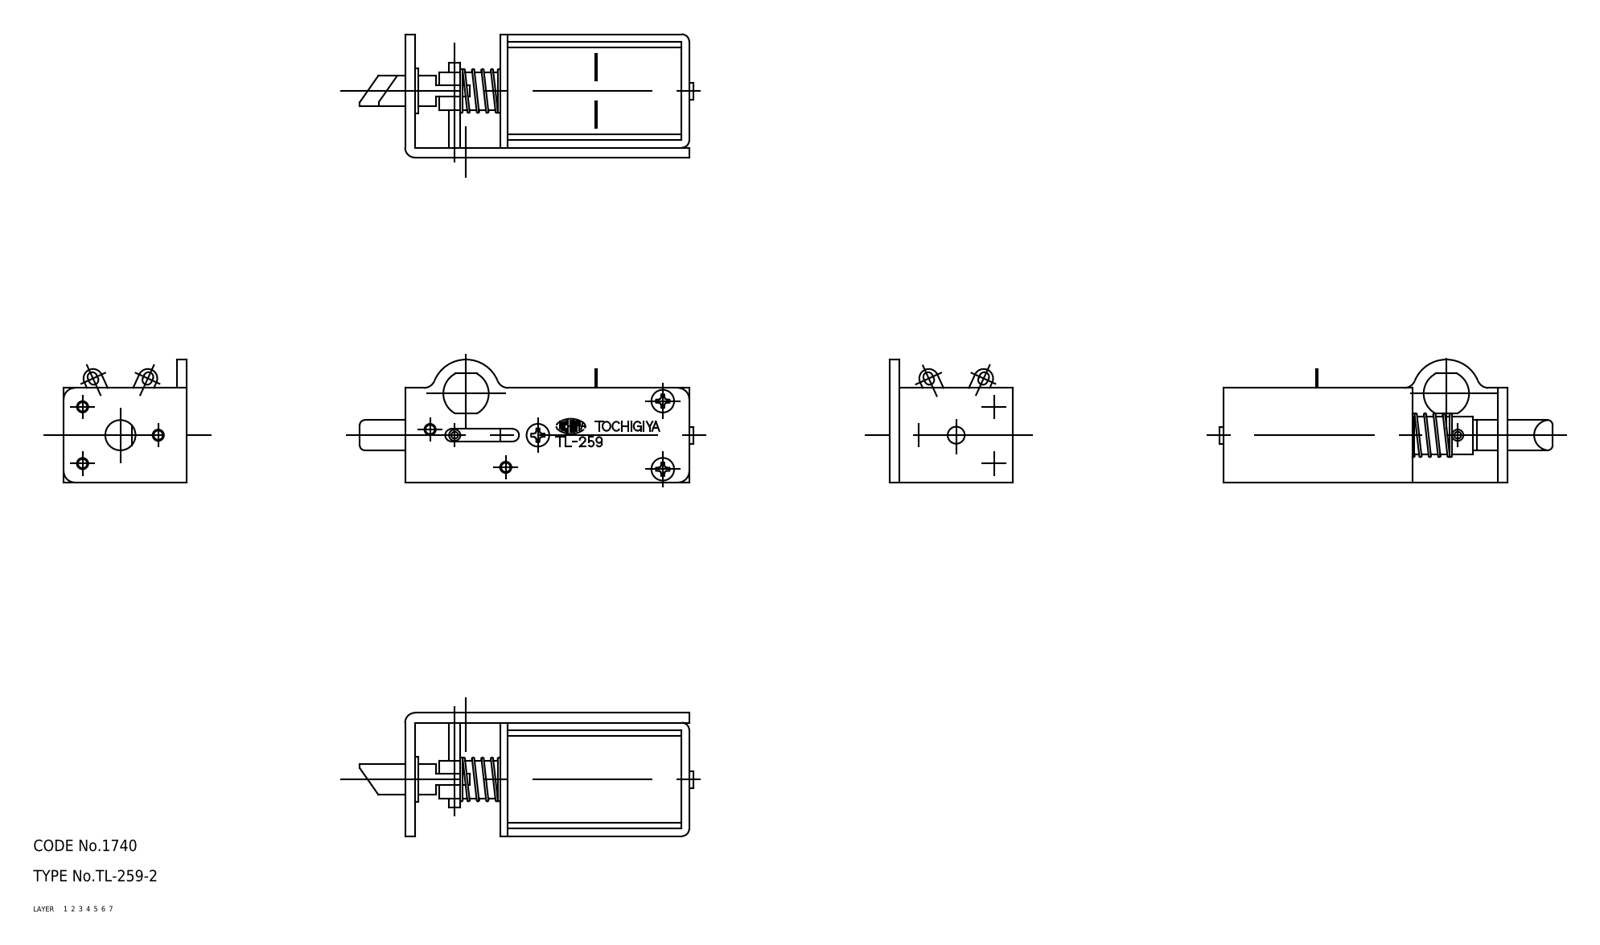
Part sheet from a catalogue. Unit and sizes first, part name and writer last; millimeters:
Units: millimetres
Overall size (bounding box): 88 × 32.5 × 32.5
Volume: 30 608 mm³ · Surface area: 19 801 mm²
Bodies: 10 solids, 249 faces (0 planar, 0 cylindrical, 249 other)
Part name (STEP PRODUCT): screw; spring; solenoid_2; solenoid_1 (+5 more)
STEP written by: CADfix (AUTOMOTIVE_DESIGN)
